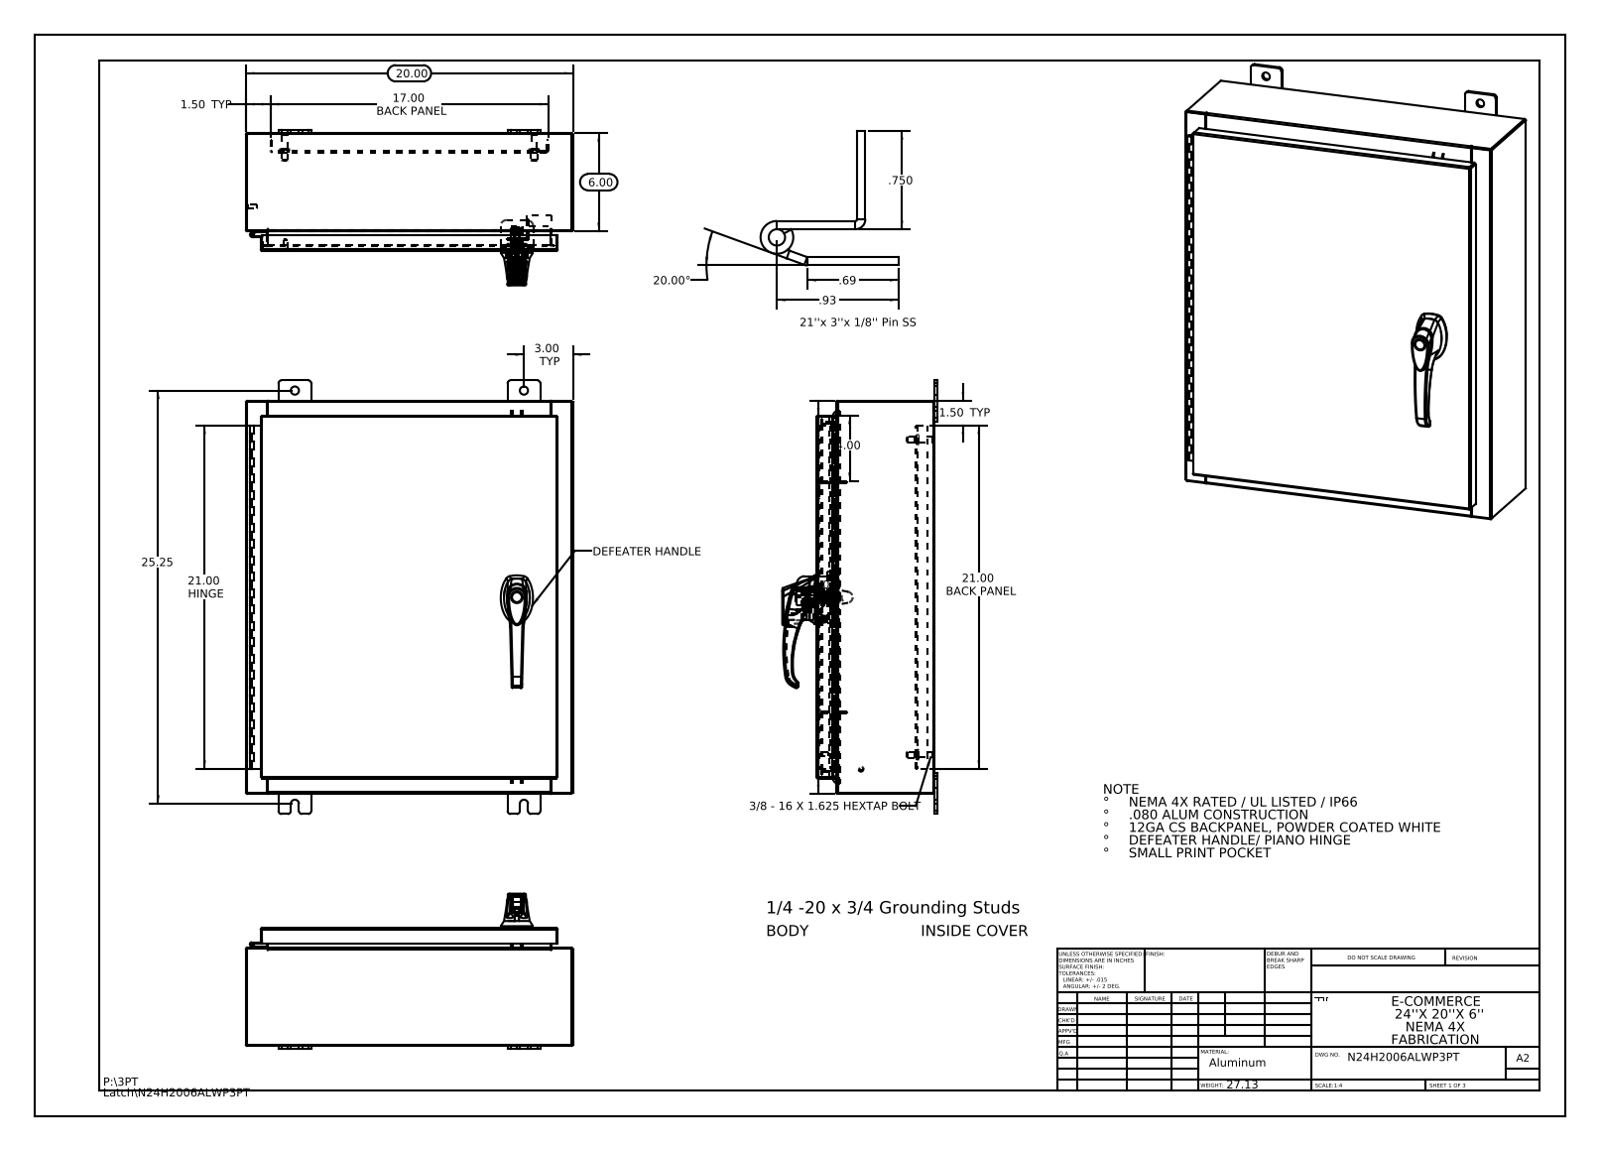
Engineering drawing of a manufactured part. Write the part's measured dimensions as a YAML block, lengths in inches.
part_name: "N24H2006ALWP3PT Defeater Handle - 3 - 2500-51 ZN; 26161102; 297026; N24H2006ALWP3PT Hinge Enclosure Side2 (+8 more)"
step_written_by: "SolidWorks 2013 (CONFIG_CONTROL_DESIGN)"
units: inches
bodies: {solids: 37, faces: 2498, planar: 883, cylindrical: 917, other: 698}
overall_size: [26.5, 20, 9.495]
volume: 181.2
surface_area: 4454
round_holes:
  - {diameter: 0.5, count: 8}
  - {diameter: 0.25, count: 4}
  - {diameter: 0.138, count: 3}
  - {diameter: 0.161, count: 3}
  - {diameter: 0.079, count: 2}
  - {diameter: 0.203, count: 2}
  - {diameter: 0.313, count: 2}
  - {diameter: 0.437, count: 2}
  - {diameter: 0.125, count: 1}
  - {diameter: 0.125, count: 1}
  - {diameter: 0.197, count: 1}
  - {diameter: 0.276, count: 1}
round_bosses_or_shafts:
  - {diameter: 0.625, count: 4}
  - {diameter: 0.375, count: 4}
  - {diameter: 0.33, count: 4}
  - {diameter: 0.157, count: 4}
  - {diameter: 0.14, count: 4}
  - {diameter: 0.315, count: 3}
  - {diameter: 0.236, count: 3}
  - {diameter: 1.181, count: 1}
partial_cylinders:
  - {radius: 0.118, count: 37}
  - {radius: 0.006, count: 33}
  - {radius: 0.19, count: 24}
  - {radius: 0.013, count: 22}
  - {radius: 0.088, count: 18}
  - {radius: 0.039, count: 15}
  - {radius: 0.028, count: 12}
  - {radius: 0.008, count: 6}
face_to_face_distances: [0.075, 7.126, 7.051, 7.201, 0.104, 1, 1.075, 6.051, 6.126, 1.179]
hole_center_spacings: [7.68, 0.295, 0.625, 0.841, 1.25, 1.313, 1.561, 1.858]
